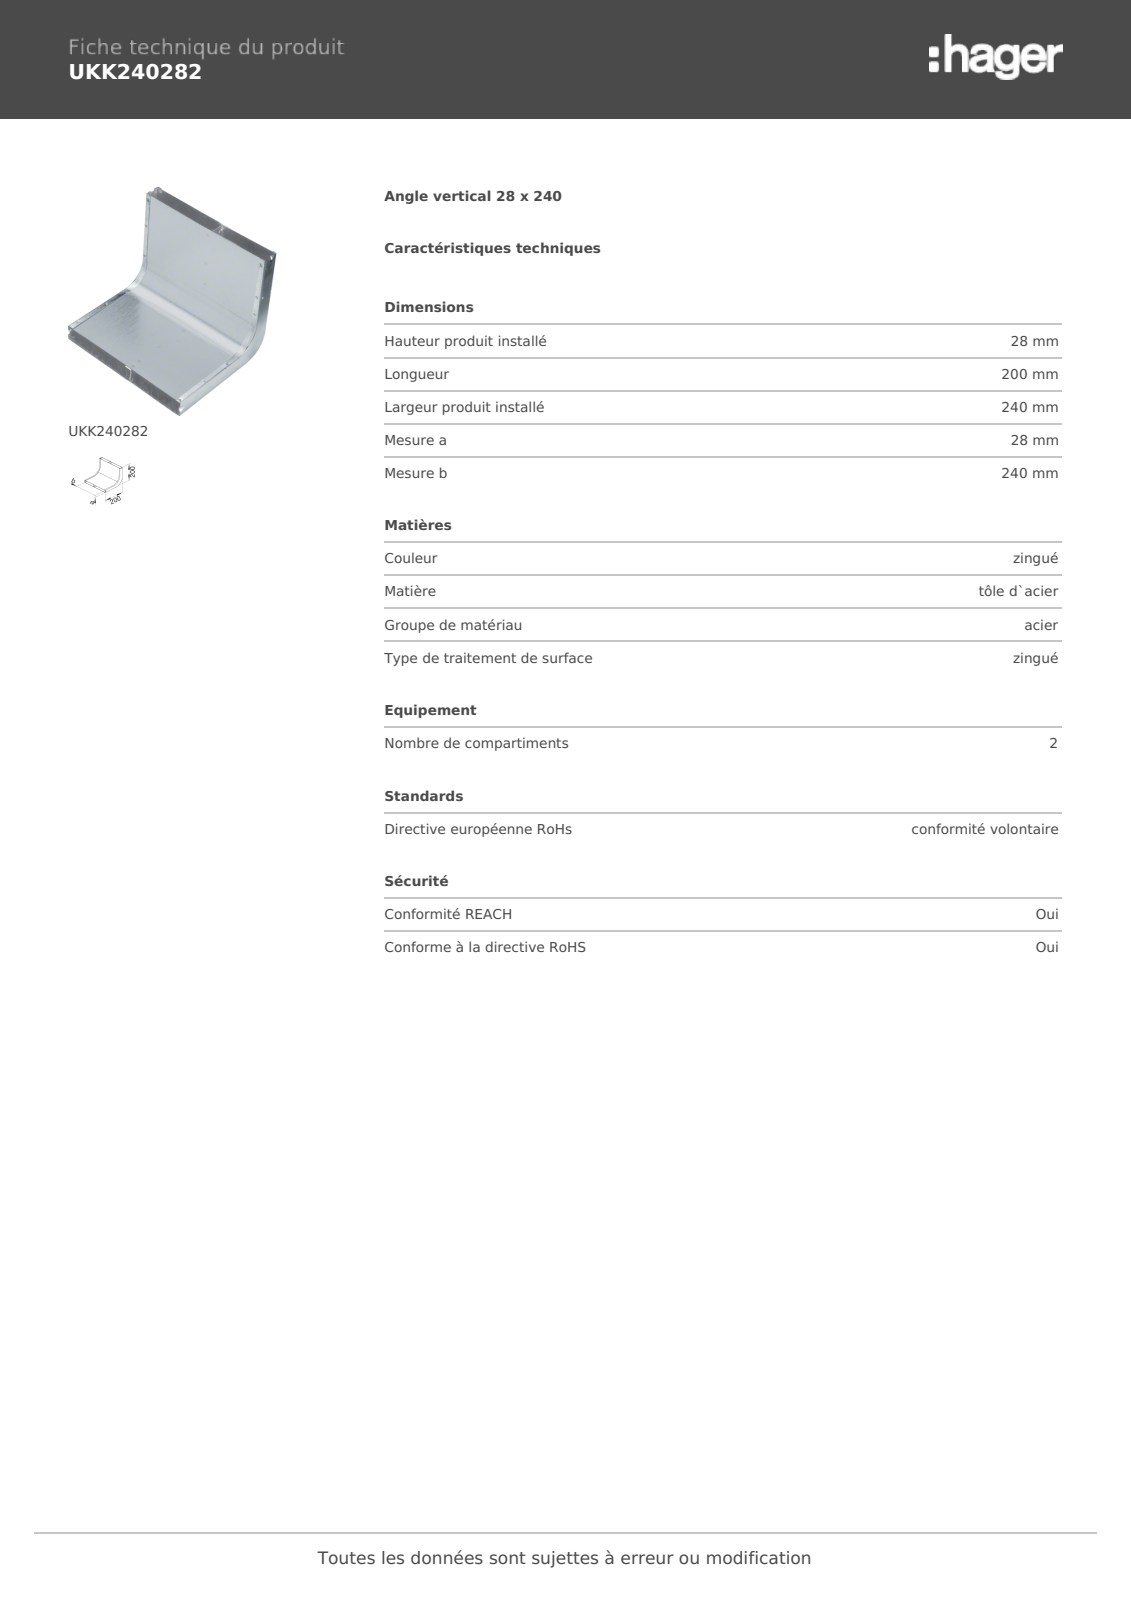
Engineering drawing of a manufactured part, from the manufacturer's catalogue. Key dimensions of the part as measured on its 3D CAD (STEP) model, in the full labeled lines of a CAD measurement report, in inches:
Part name (STEP PRODUCT): UKKI_240-28-SIMPLIFIED; UKKS_28-SIMPLIFIED; UKKA_240-SIMPLIFIED; UKKT_28-SIMPLIFIED (+1 more)
STEP written by: CREO PARAMETRIC BY PTC INC, 2022024 (AUTOMOTIVE_DESIGN)
Units: inches
Bodies: 5 solids, 62 faces (49 planar, 13 cylindrical, 0 other)
Overall size (bounding box): 9.449 × 7.895 × 7.894
Volume: 9.899 in³ · Surface area: 676.2 in²
Partial cylindrical surfaces — rounded edges, fillets, slot ends (radius × count): R0.039 ×5, R0.069 ×3, R0.01 ×1
Main face-to-face distances: 0.03, 1.014, 0.984, 1.043, 9.419, 5.453, 3.967, 9.449, 9.39, 5.423
